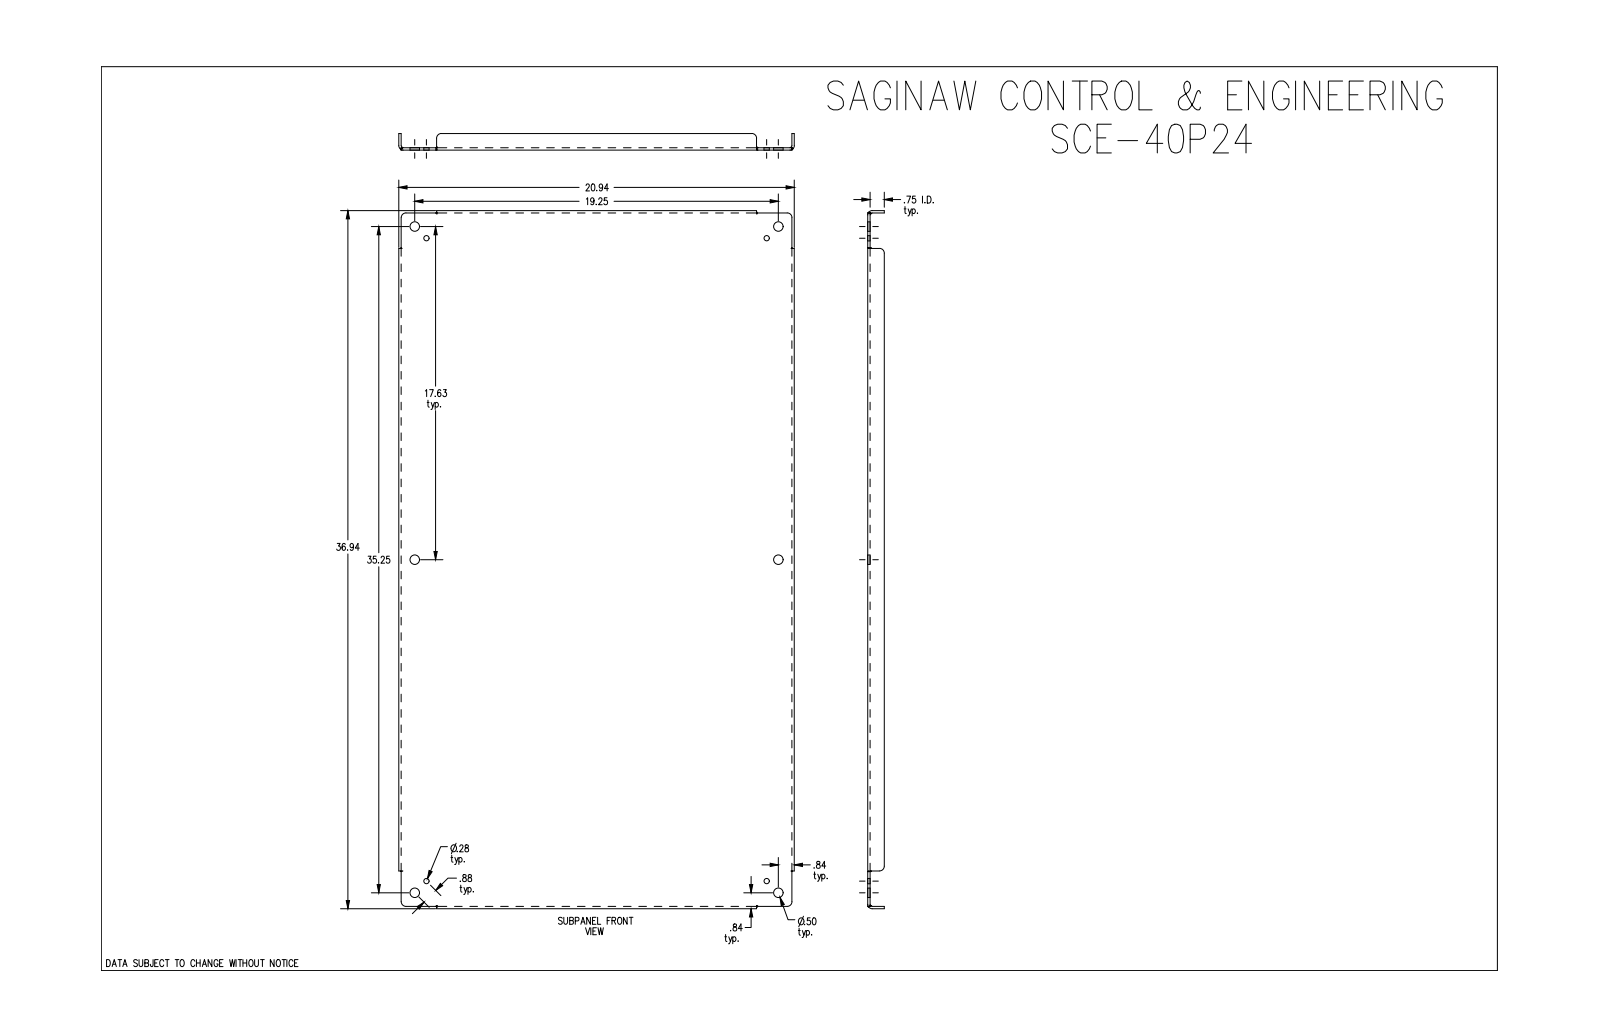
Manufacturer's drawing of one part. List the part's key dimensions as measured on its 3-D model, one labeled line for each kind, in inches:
Part name (STEP PRODUCT): SCE-40P24
STEP written by: SolidWorks 2019 (CONFIG_CONTROL_DESIGN)
Units: inches
Bodies: 1 solid, 84 faces (30 planar, 30 cylindrical, 24 other)
Overall size (bounding box): 36.938 × 20.938 × 0.875
Volume: 104.6 in³ · Surface area: 1 691 in²
Round holes (diameter × count): ⌀0.5 ×6, ⌀0.281 ×4
Partial cylindrical surfaces — rounded edges, fillets, slot ends (radius × count): R0.25 ×8, R0.112 ×4, R0.237 ×4
Main face-to-face distances: 0.125, 0.125, 20.813, 36.813, 20.687, 20.938, 0.75, 0.875, 36.687, 36.938
Hole centre spacings: 0.875, 17.018, 17.625, 18.641, 25.226, 26.1, 34.637, 39.325
